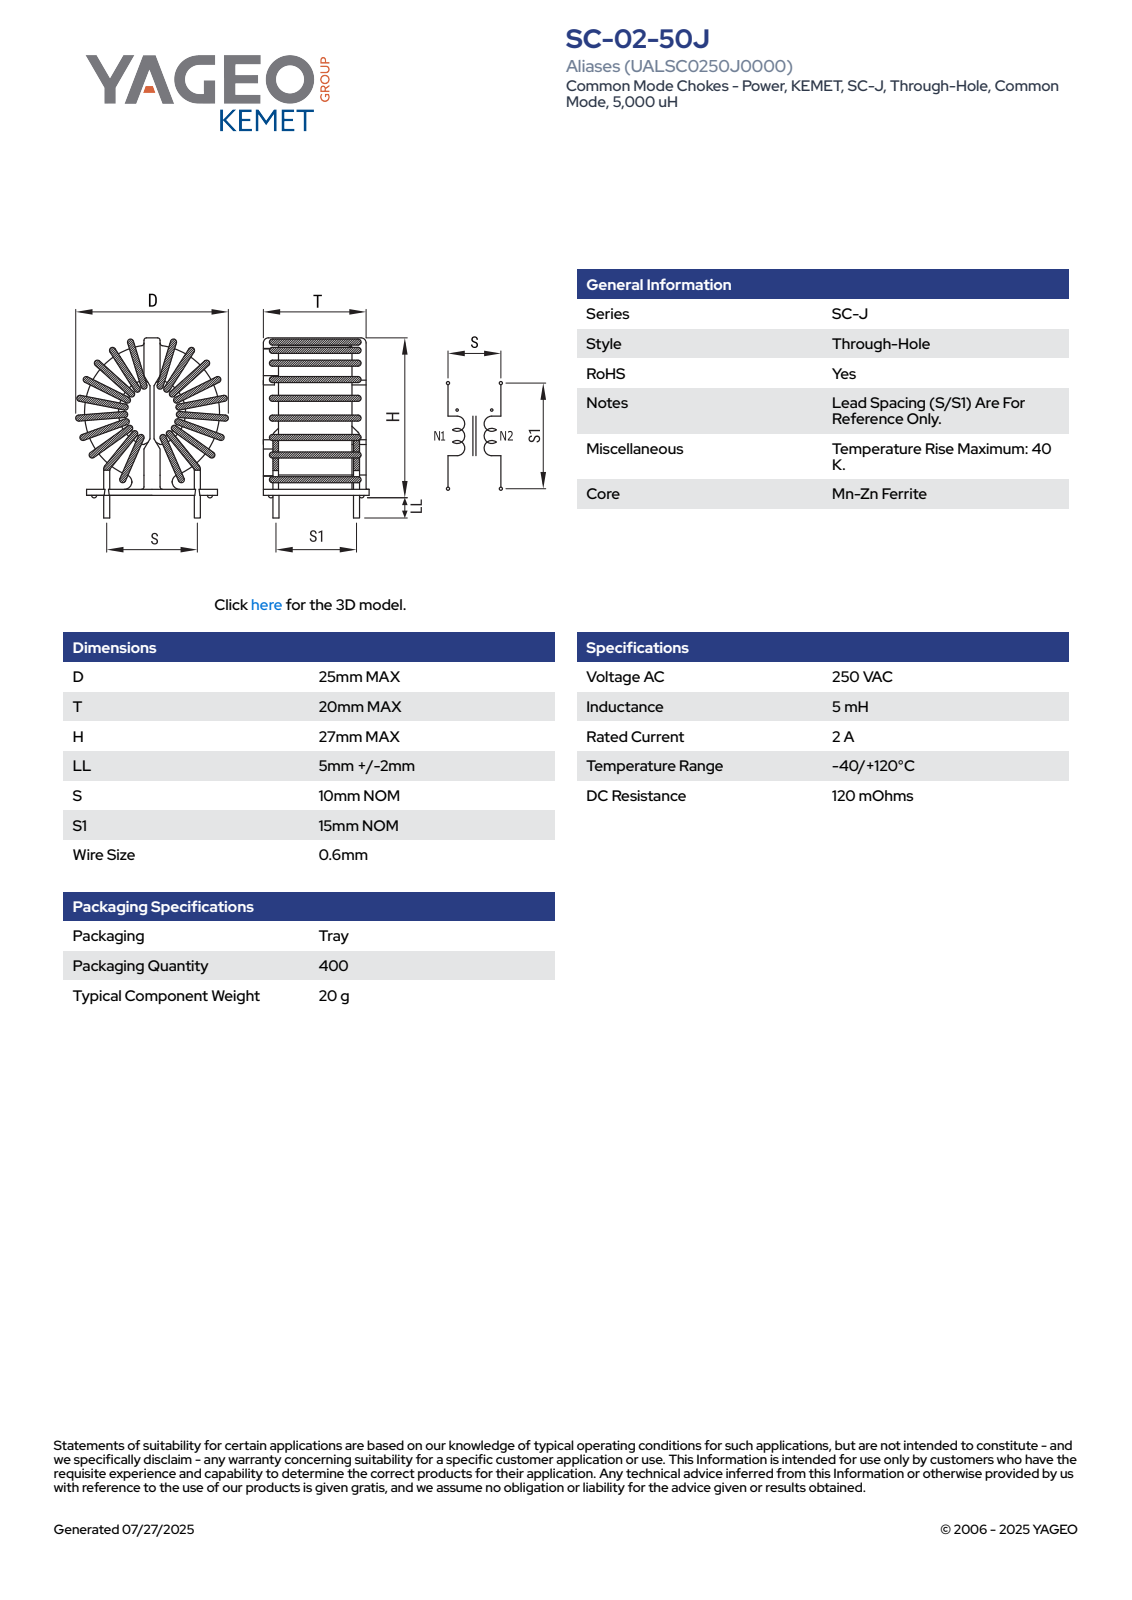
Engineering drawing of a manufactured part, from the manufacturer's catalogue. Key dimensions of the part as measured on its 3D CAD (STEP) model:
Part name (STEP PRODUCT): SC-02-50J
STEP written by: SolidWorks 2018 (AUTOMOTIVE_DESIGN)
Units: millimetres
Bodies: 1 solid, 334 faces (141 planar, 113 cylindrical, 80 other)
Overall size (bounding box): 31.5 × 25 × 20
Volume: 9 040 mm³ · Surface area: 4 710 mm²
Round bosses / shafts (diameter × count): ⌀0.6 ×8, ⌀1 ×4
Partial cylindrical surfaces — rounded edges, fillets, slot ends (radius × count): R0.5 ×21, R0.3 ×16, R1 ×6, R0.42 ×4, R1.5 ×4, R0.9 ×2, R3.09 ×1, R4.39 ×1
Main face-to-face distances: 2.35, 19, 1.2, 2, 3.2, 0.8, 12.6, 0.5, 19.5, 9.4
